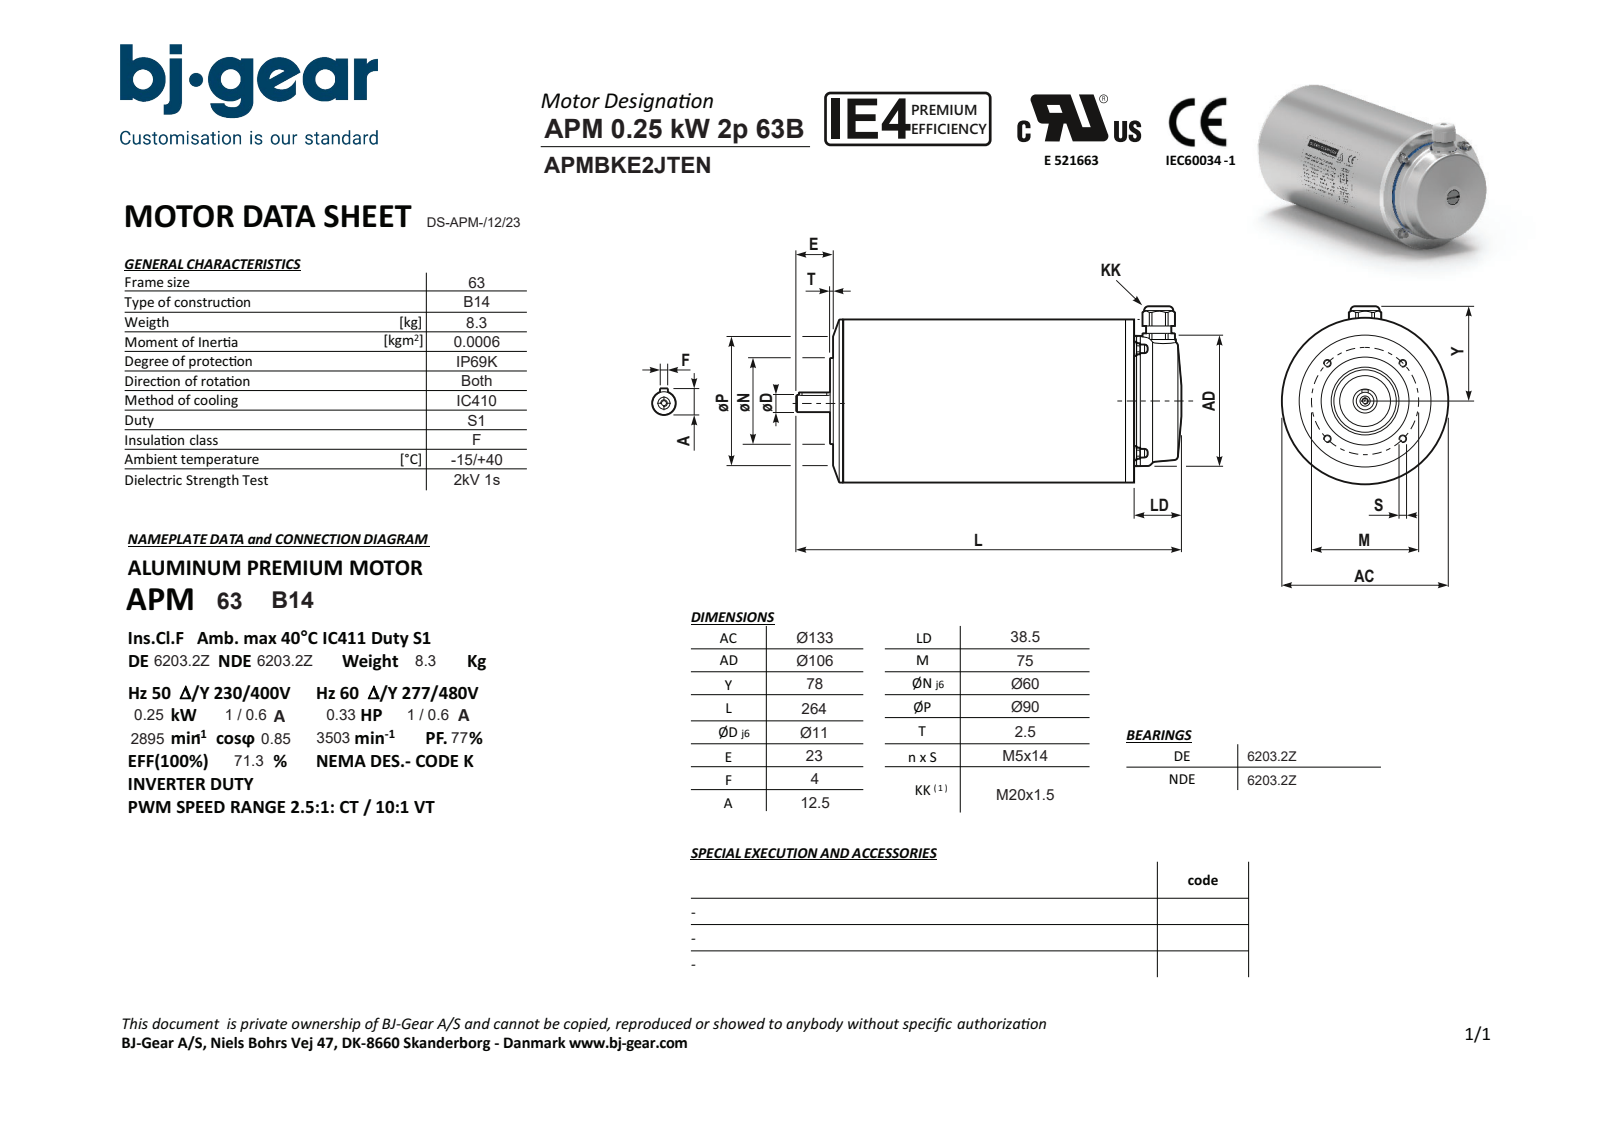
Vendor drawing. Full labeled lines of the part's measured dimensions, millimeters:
Part name (STEP PRODUCT): APMBKE2JTENN4KCR2-N---NNN
STEP written by: Solid Edge (AUTOMOTIVE_DESIGN)
Units: millimetres
Bodies: 1 solid, 156 faces (71 planar, 50 cylindrical, 35 other)
Overall size (bounding box): 264 × 143.3 × 132.6
Volume: 3 075 000 mm³ · Surface area: 127 331 mm²
Round holes (diameter × count): ⌀4.13 ×4, ⌀3.24 ×1, ⌀4.3 ×1, ⌀16 ×1, ⌀28 ×1, ⌀52 ×1
Round bosses / shafts (diameter × count): ⌀11.5 ×4, ⌀7 ×4, ⌀132.6 ×1, ⌀132.6 ×1, ⌀106 ×1, ⌀60 ×1, ⌀23.7 ×1, ⌀20.6 ×1
Partial cylindrical surfaces — rounded edges, fillets, slot ends (radius × count): R2 ×2, R13.2 ×1
Main face-to-face distances: 202.5, 197, 5.5, 8, 2.5, 205, 38.5, 235.5, 241, 243.5
Hole centre spacings: 37.5, 53.04, 75.01
